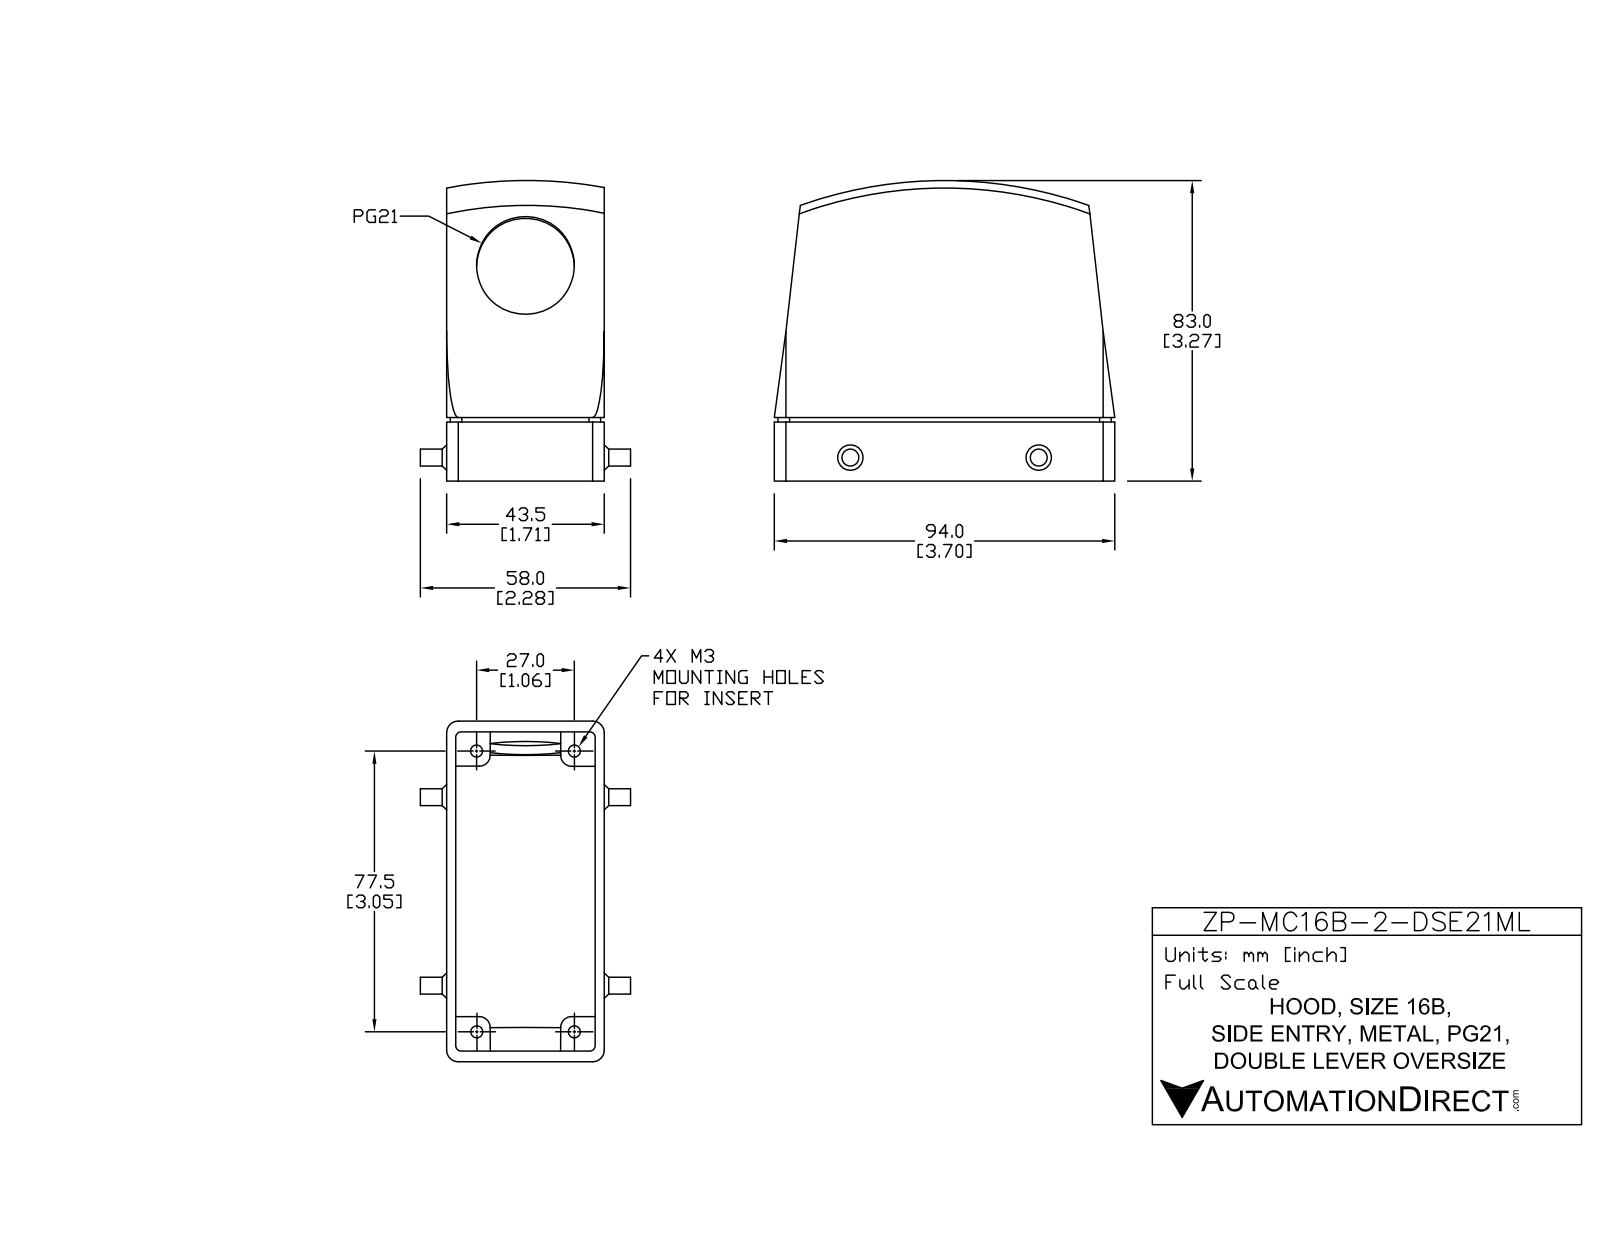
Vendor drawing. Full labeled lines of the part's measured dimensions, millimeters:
Part name (STEP PRODUCT): ZP-MC16B-2-DSE21ML
STEP written by: SolidWorks 2011 (AUTOMOTIVE_DESIGN)
Units: millimetres
Bodies: 9 solids, 104 faces (60 planar, 34 cylindrical, 10 other)
Overall size (bounding box): 94 × 77.55 × 58
Volume: 67 049 mm³ · Surface area: 51 791 mm²
Round holes (diameter × count): ⌀3.5 ×4, ⌀27 ×1
Round bosses / shafts (diameter × count): ⌀4.67 ×2
Partial cylindrical surfaces — rounded edges, fillets, slot ends (radius × count): R3.2 ×8, R1.5 ×4, R3 ×4, R0.7 ×1
Main face-to-face distances: 2.5, 41, 43.5, 38.5, 9.5, 2.96, 91.04, 78.58, 81.54, 12.46
Hole centre spacings: 28.96, 79.5, 84.61
